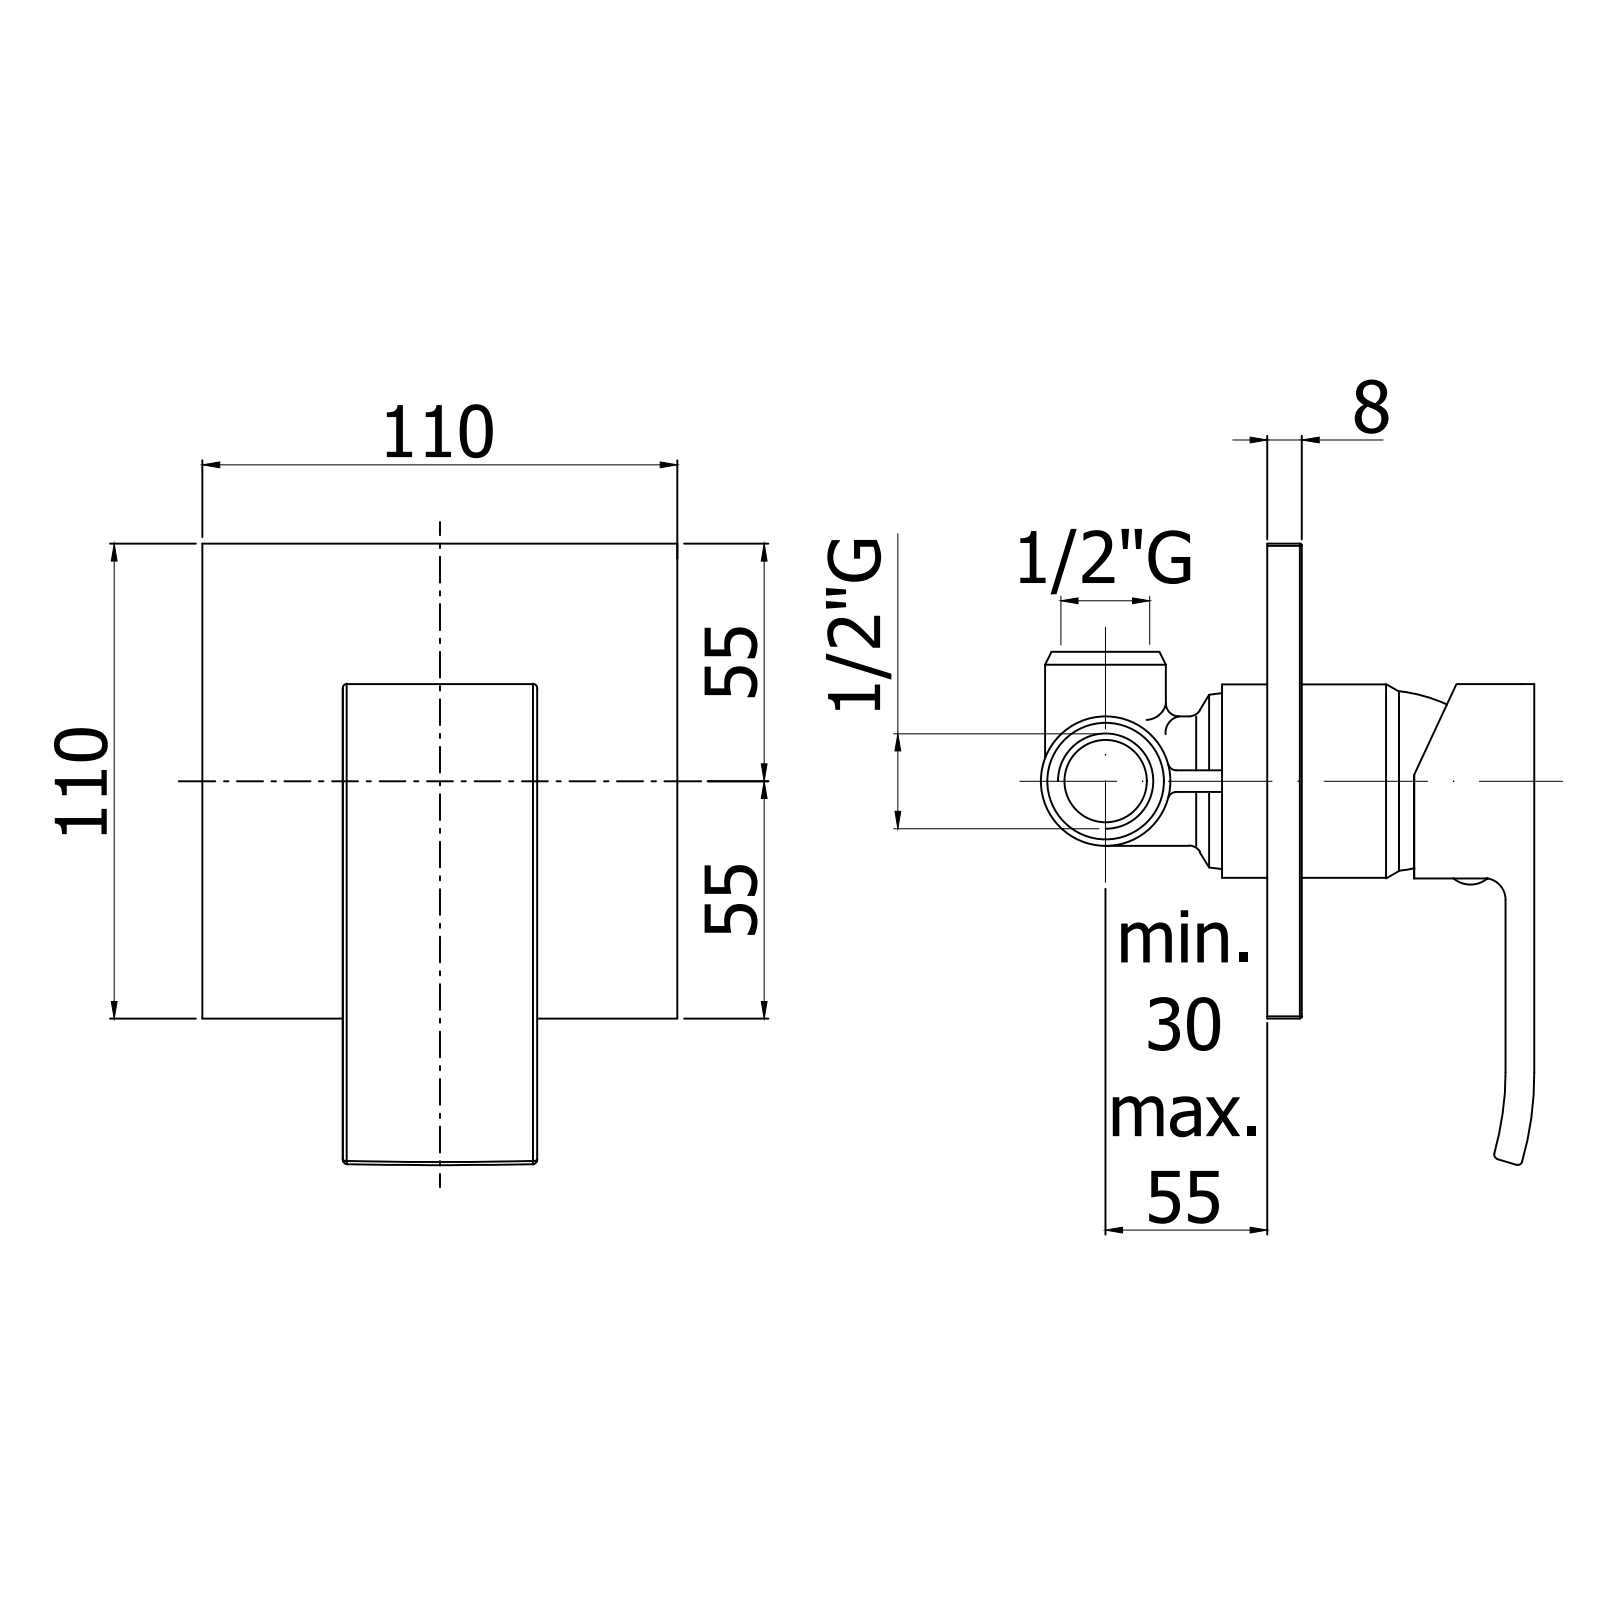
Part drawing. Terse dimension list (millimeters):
name: LES010CR
written by: CREO PARAMETRIC BY PTC INC, 2020044 (CONFIG_CONTROL_DESIGN)
unit: mm
bodies: 2 solids, 939 faces (570 planar, 222 cylindrical, 147 other)
size: 144.07 × 110 × 55.1
volume: 121 713 mm³; area: 71 491 mm²
holes: 2× ⌀4, 1× ⌀3, 1× ⌀5, 1× ⌀5.5, 1× ⌀7.8, 1× ⌀19.5, 1× ⌀19.9, 1× ⌀26.8, 1× ⌀29, 1× ⌀31, 1× ⌀32.4, 1× ⌀36
bosses: 1× ⌀51, 1× ⌀49, 1× ⌀44.8, 1× ⌀35, 1× ⌀23.5, 1× ⌀23.4, 1× ⌀21.8, 1× ⌀7.6
rounds: 34× R0.5, 14× R1.5, 11× R0.15, 8× R2, 6× R1, 4× R0.3, 2× R300, 1× R2.25
face distances: 7, 2, 32.5, 77.5, 0.5, 5, 2.5, 30.5, 108, 75.5
hole spacings: 8
